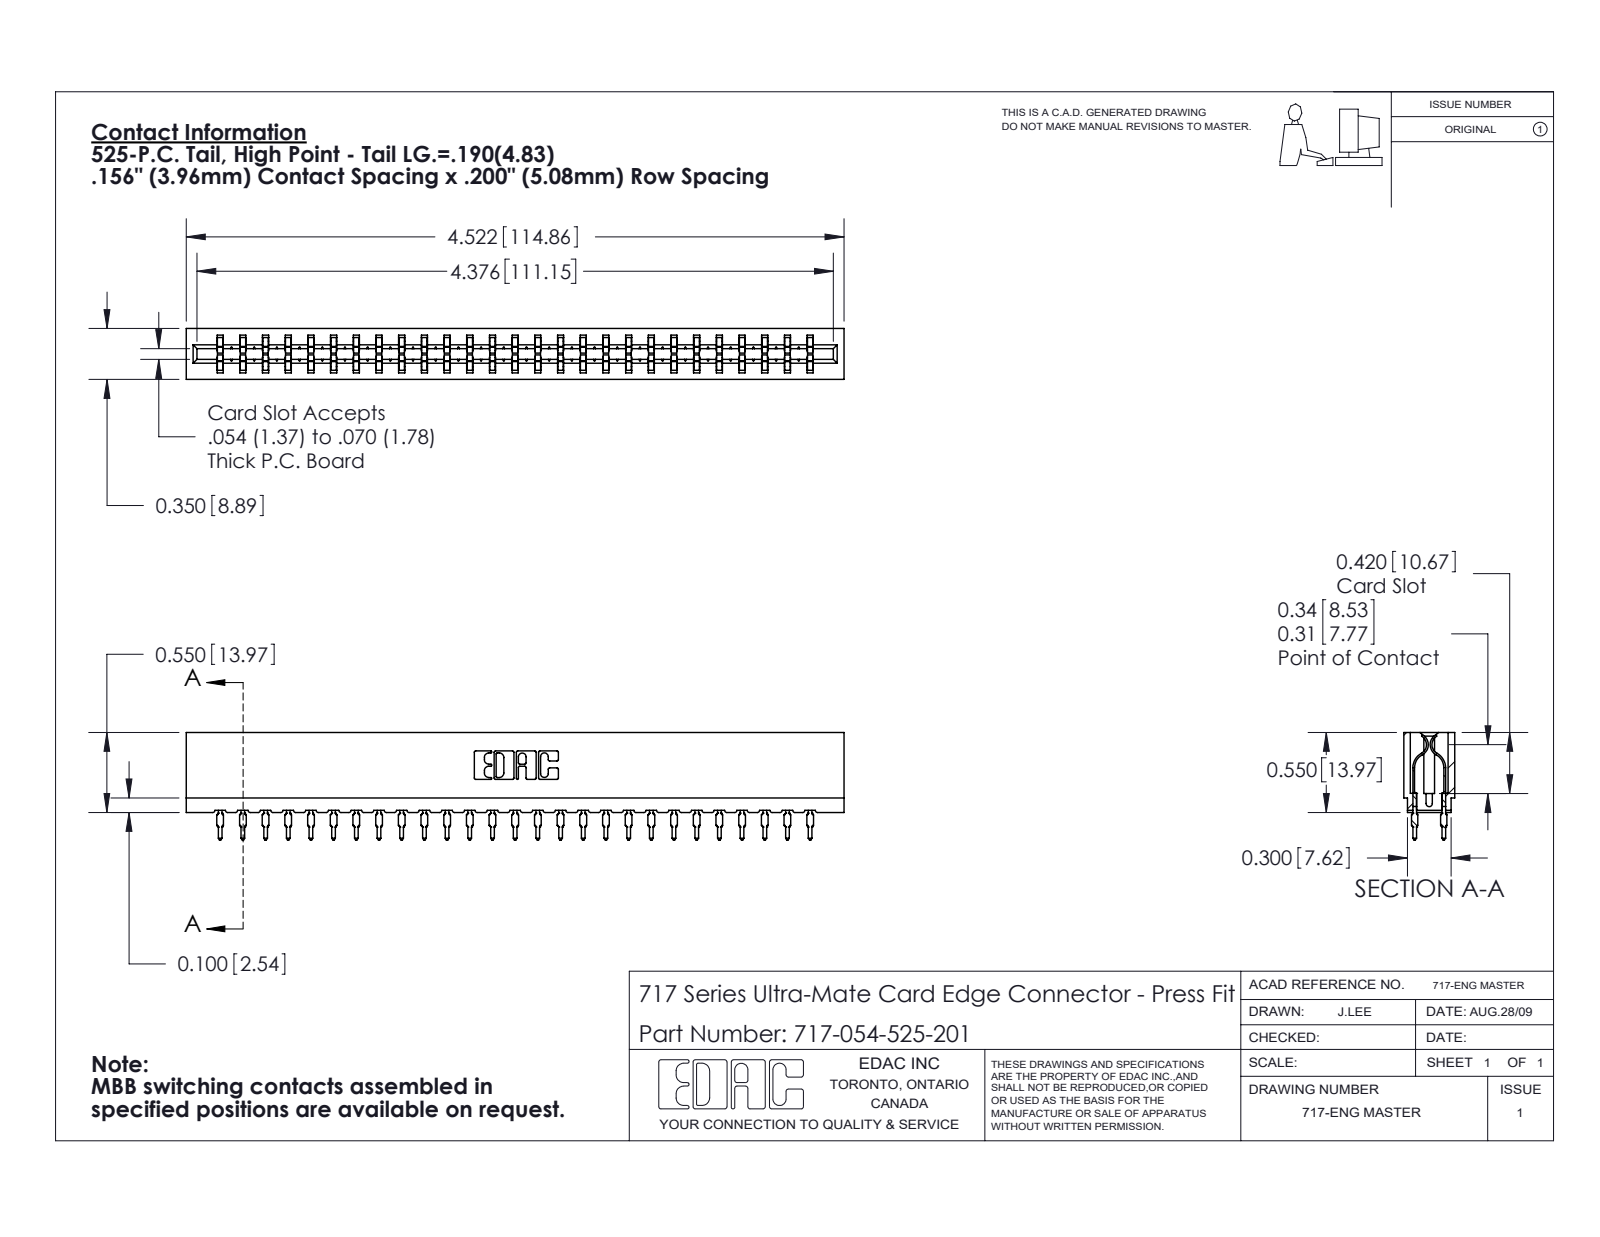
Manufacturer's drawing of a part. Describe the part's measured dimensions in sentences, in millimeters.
The part is named "717 Part_Insulator Option - 06; 717-054-525-201; 745-292-001_525". Its 3-D file was written by "SolidWorks 2020 (CONFIG_CONTROL_DESIGN)". It is 55 solids with 4954 faces: 2565 planar, 985 cylindrical and 1404 other. Overall it measures 114.9 by 18.8 by 8.9 millimeters. Its volume is 10 000 cubic millimeters and its surface area 15 040 square millimeters. Partial cylindrical surfaces (rounded edges, fillets, slot ends): 108 of radius 0.5, 54 of radius 0.4, 22 of radius 0.3, 8 of radius 0.1, 8 of radius 0.3, 6 of radius 0.2, 6 of radius 0.8, 3 of radius 0.7. The main face-to-face distances are 5.4, 3.5, 8.9, 1.6, 7.3, 1.9, 3.8, 4, 1.9, 1.1.
